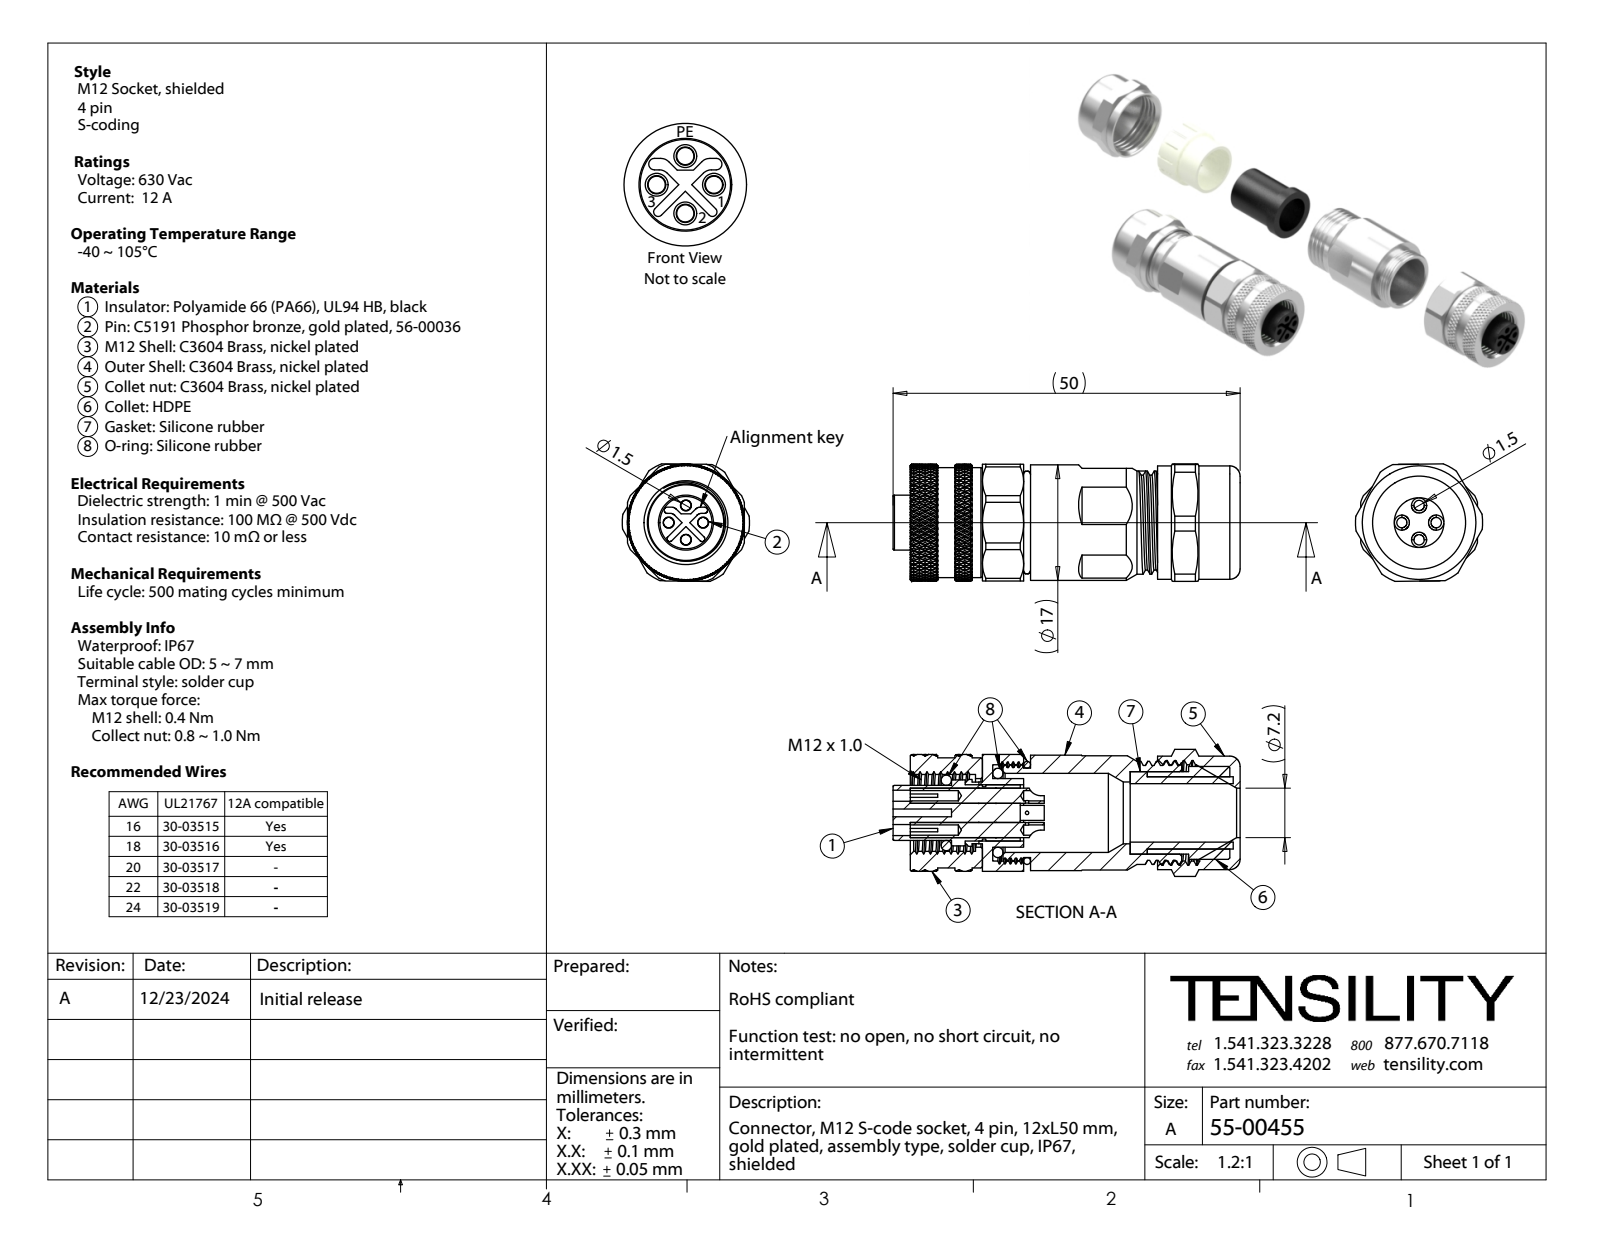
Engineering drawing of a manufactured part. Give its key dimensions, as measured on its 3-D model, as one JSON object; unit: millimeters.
{"part_name": "55-00455-07; 55-00455-03; 55-00455; 55-00455-04 (+8 more)", "step_written_by": "SolidWorks 2021 (CONFIG_CONTROL_DESIGN)", "units": "millimeters", "bodies": {"solids": 14, "faces": 540, "planar": 196, "cylindrical": 208, "other": 136}, "overall_size": [50.5, 18.5, 17.11], "volume_mm3": 7408, "surface_area_mm2": 11652, "round_holes": [[1.5, 4], [1.6, 4], [0.5, 2], [7.2, 1], [7.6, 1], [8.2, 1], [8.5, 1], [9, 1], [10, 1], [10.5, 1], [11.2, 1], [11.5, 1]], "round_bosses_or_shafts": [[2.2, 4], [17, 1], [16.8, 1], [16.5, 1], [16, 1], [15, 1], [13.5, 1], [13, 1]], "partial_cylinders_radius": [[1, 4], [1.86, 4], [0.4, 2], [0.45, 2], [9, 1], [9.25, 1]], "face_to_face_distances": [17, 1.5, 6, 16, 1, 10.5, 30.5, 34.5, 7, 4.5], "hole_center_spacings": [2.5, 3.54, 5]}
